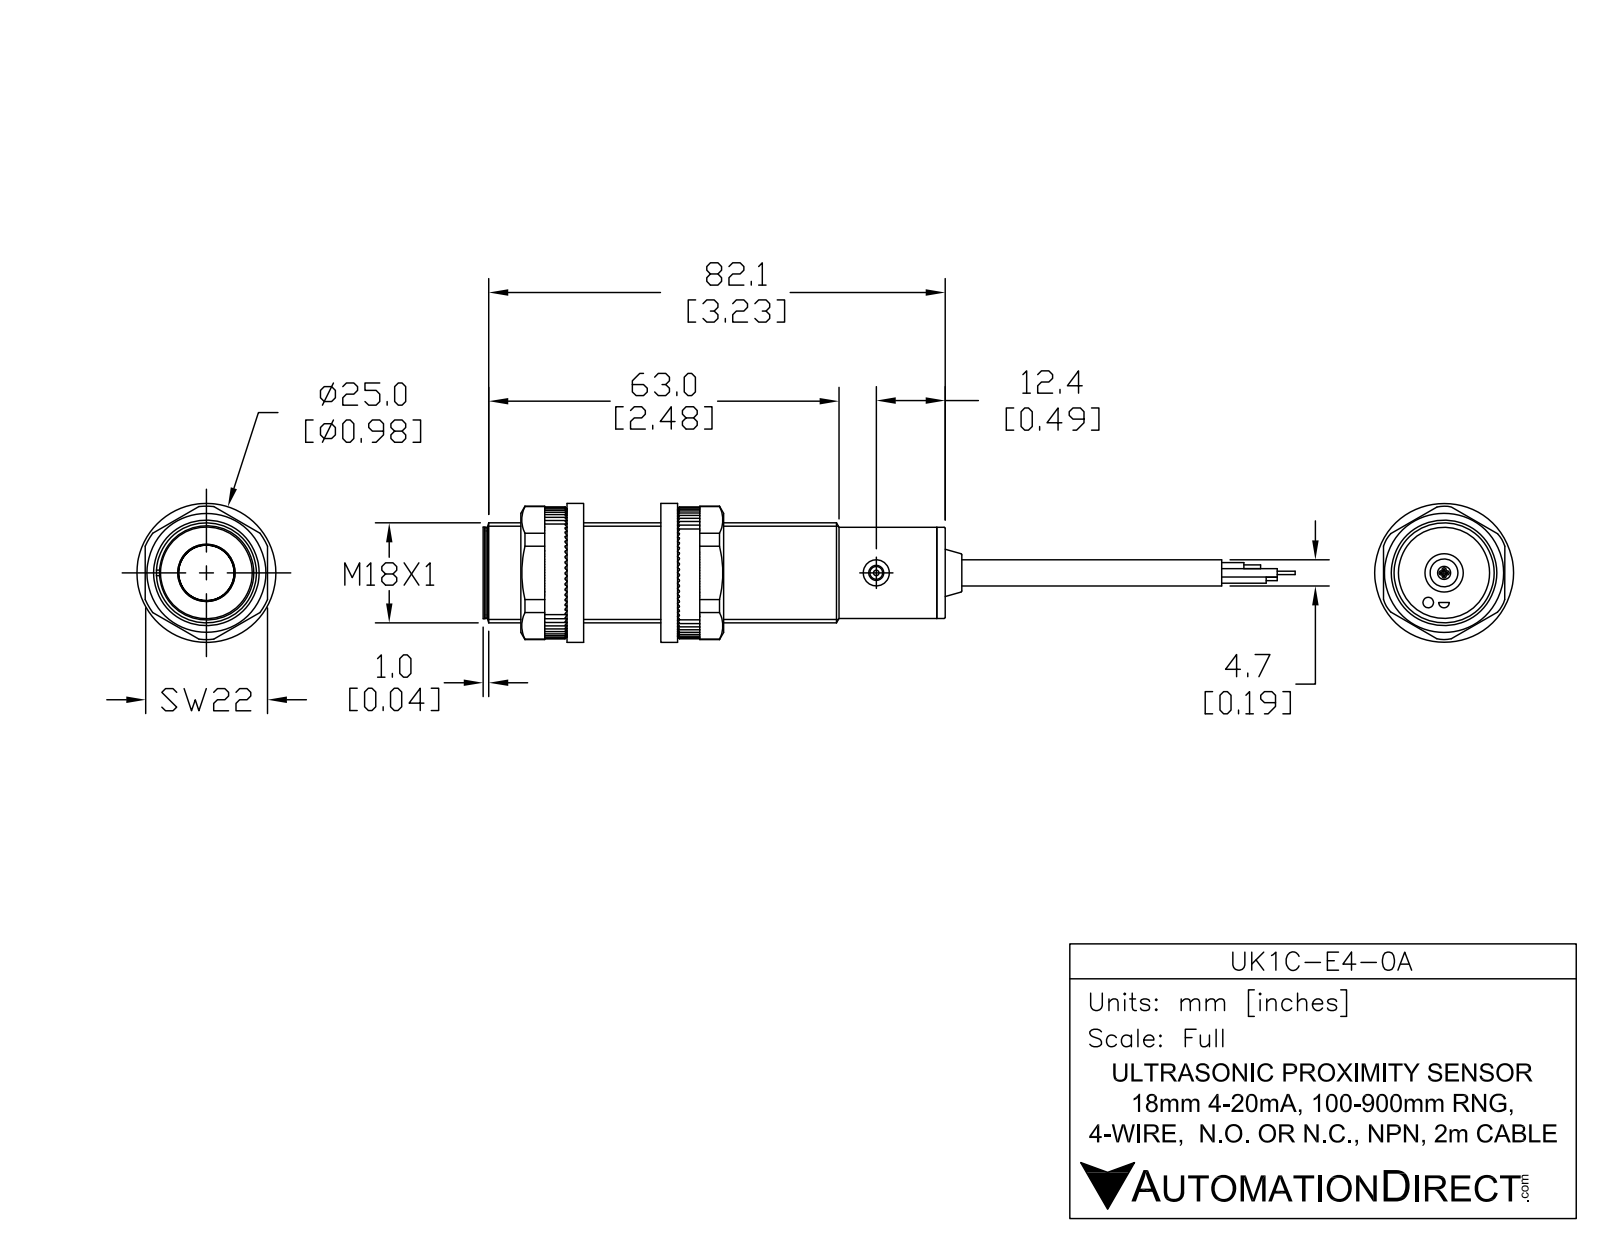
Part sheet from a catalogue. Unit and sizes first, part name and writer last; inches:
Units: inches
Overall size (bounding box): 4.832 × 0.709 × 0.709
Round holes (diameter × count): ⌀0.185 ×2, ⌀0.106 ×1
Round bosses / shafts (diameter × count): ⌀0.709 ×1, ⌀0.646 ×1, ⌀0.622 ×1, ⌀0.374 ×1, ⌀0.189 ×1, ⌀0.091 ×1
Main face-to-face distances: 3.193, 3.252, 0.059, 0.039, 3.232, 3.291, 0.041, 3.234, 3.293, 3.257
Volume: 1.285 in³ · Surface area: 10.69 in²
Bodies: 6 solids, 55 faces (17 planar, 24 cylindrical, 14 other)
Part name (STEP PRODUCT): UK1C-E4-0A
STEP written by: SolidWorks 2017 (AUTOMOTIVE_DESIGN)
